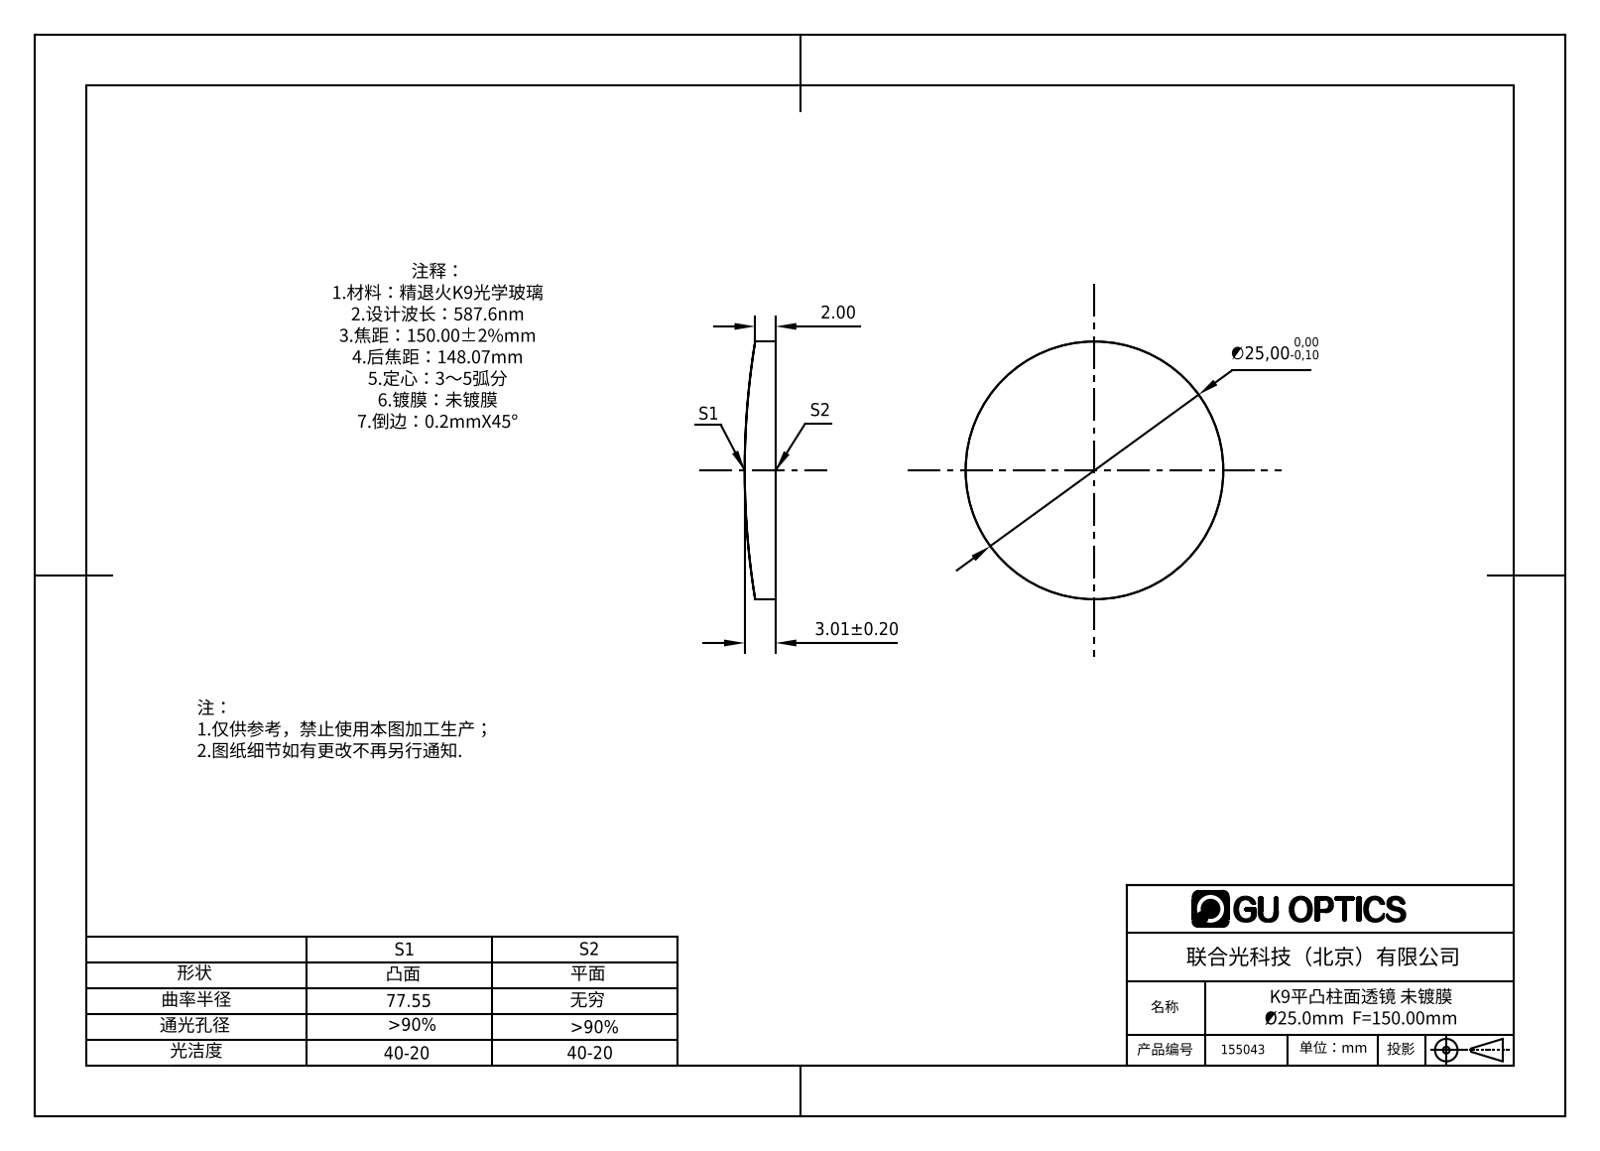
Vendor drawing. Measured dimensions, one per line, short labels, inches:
name: 155043
written by: SolidWorks 2016 (AUTOMOTIVE_DESIGN)
unit: in
bodies: 1 solid, 4 faces (1 planar, 3 cylindrical, 0 other)
size: 0.984 × 0.984 × 0.119
volume: 0.083 in³; area: 1.829 in²
bosses: 1× ⌀0.984
rounds: 1× R3.053
